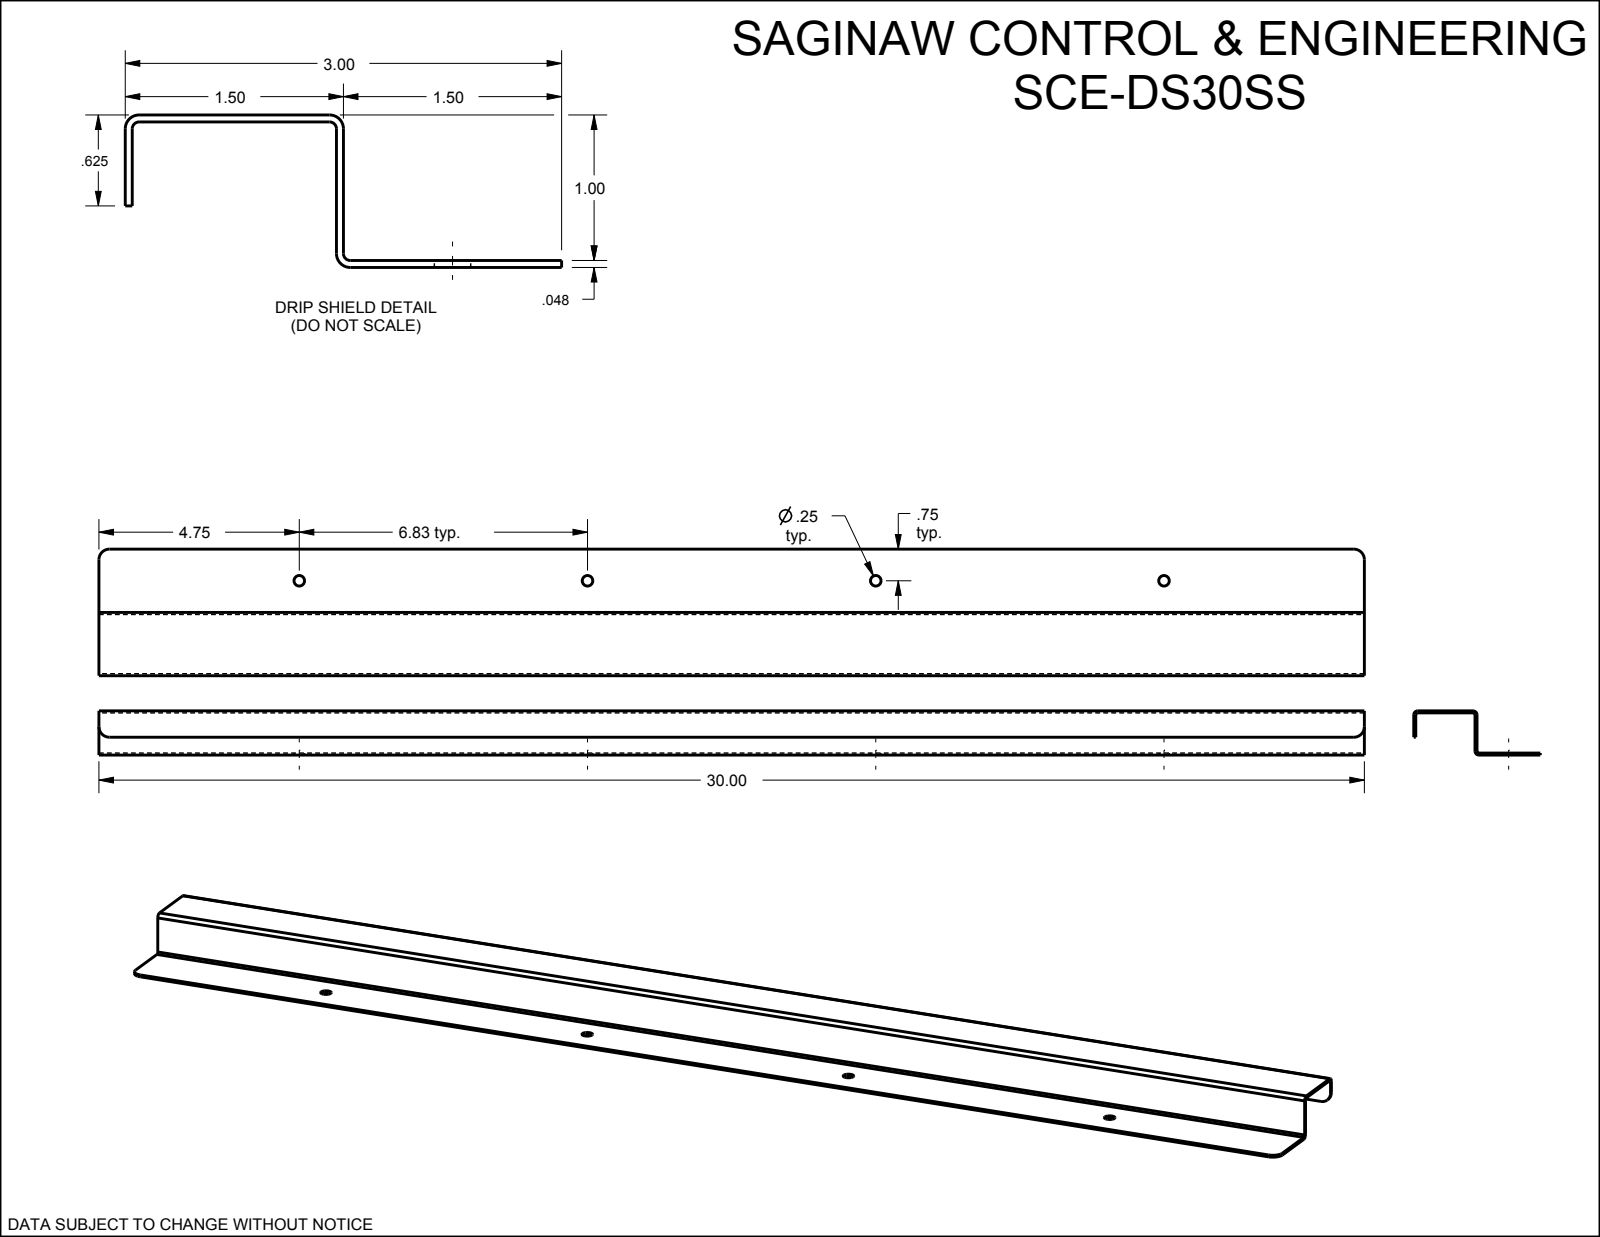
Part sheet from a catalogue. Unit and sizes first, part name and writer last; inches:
Units: inches
Overall size (bounding box): 30 × 3 × 1.048
Round holes (diameter × count): ⌀0.25 ×4
Partial cylindrical surfaces — rounded edges, fillets, slot ends (radius × count): R0.25 ×4, R0.047 ×3, R0.095 ×3
Main face-to-face distances: 0.048, 1, 1.048, 0.952, 1.452, 1.5, 1.404, 0.423, 0.375, 0.577
Hole centre spacings: 6.833, 13.667, 6.833, 20.5
Volume: 6.447 in³ · Surface area: 272.1 in²
Bodies: 1 solid, 26 faces (12 planar, 14 cylindrical, 0 other)
Part name (STEP PRODUCT): SCE-DS30SS
STEP written by: SolidWorks 2019 (CONFIG_CONTROL_DESIGN)
